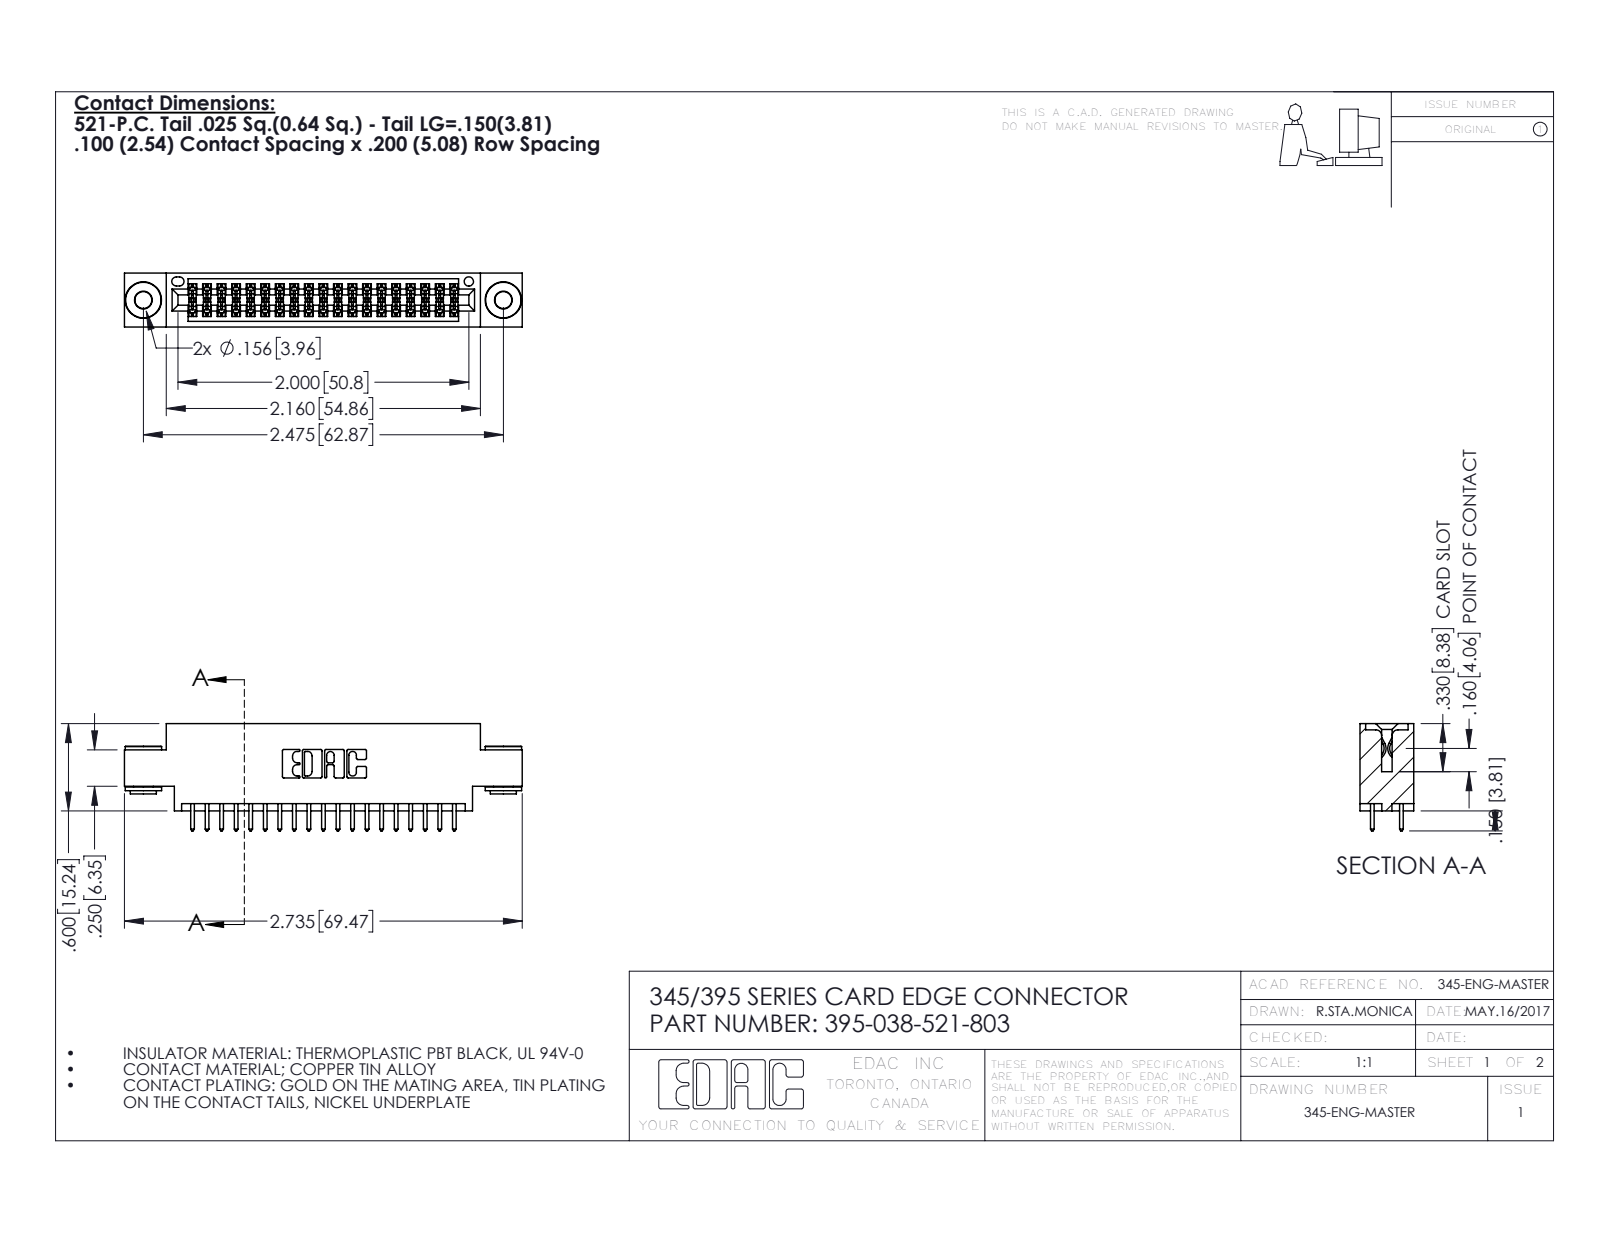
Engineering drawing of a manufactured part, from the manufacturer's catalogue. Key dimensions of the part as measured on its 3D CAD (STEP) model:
Part name (STEP PRODUCT): 395-038-521-803; 345-292-001_345-293-121; 345-250-002_345-250-002-102; 345 Part_0.170 Offset - 0.156 Dia-TH
STEP written by: SolidWorks 2016 (CONFIG_CONTROL_DESIGN)
Units: inches
Bodies: 41 solids, 2068 faces (1348 planar, 712 cylindrical, 8 other)
Overall size (bounding box): 2.735 × 0.737 × 0.37
Volume: 0.392 in³ · Surface area: 14.41 in²
Round holes (diameter × count): ⌀0.116 ×2, ⌀0.156 ×2, ⌀0.064 ×1
Round bosses / shafts (diameter × count): ⌀0.25 ×2, ⌀0.18 ×2, ⌀0.136 ×2
Partial cylindrical surfaces — rounded edges, fillets, slot ends (radius × count): R0.006 ×57, R0.01 ×38, R0.01 ×22, R0.007 ×6, R0.031 ×6, R0.026 ×3, R0.014 ×2, R0.019 ×2
Main face-to-face distances: 0.072, 0.298, 0.37, 0.2, 0.098, 0.272, 0.025, 0.225, 0.175, 0.1
Hole centre spacings: 0.27, 2.241, 2.475
